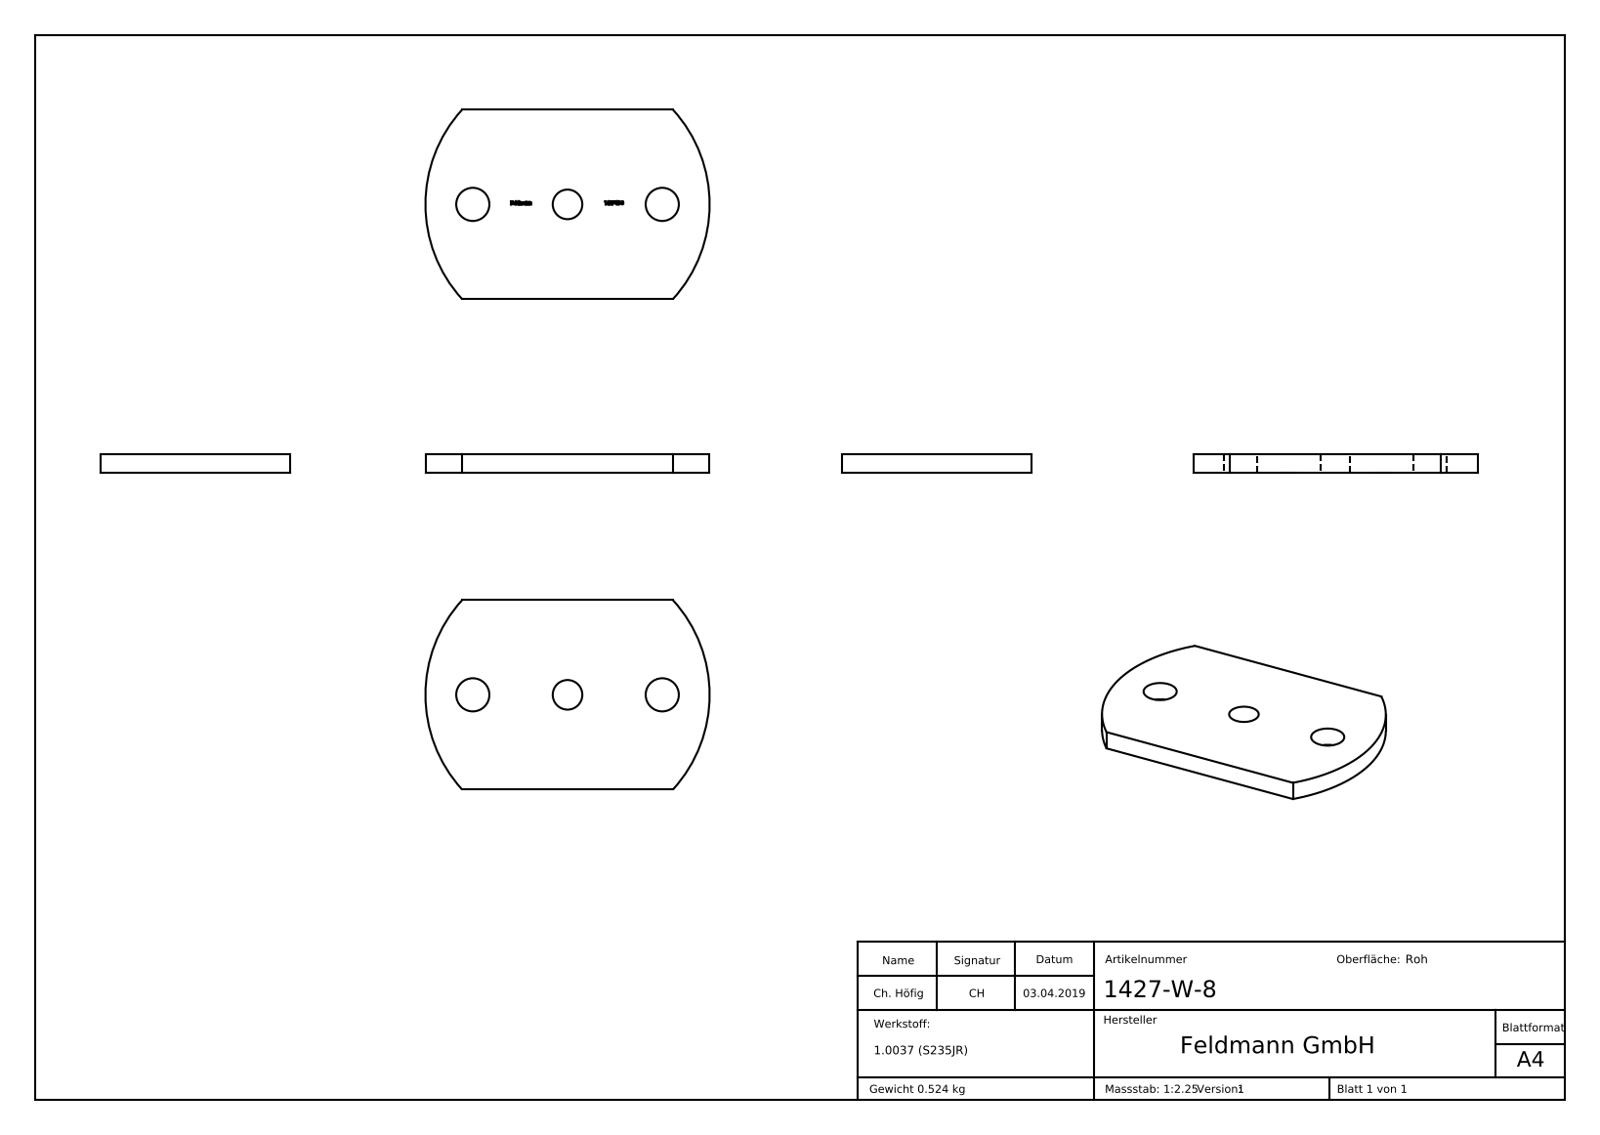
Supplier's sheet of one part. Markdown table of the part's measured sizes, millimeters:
| quantity | value |
| --- | --- |
| part name | 1427-W-8 |
| STEP written by | SolidWorks 2015 (CONFIG_CONTROL_DESIGN) |
| units | millimeters |
| bodies | 1 solid, 211 faces (132 planar, 8 cylindrical, 71 other) |
| overall size | 120 × 80 × 8 |
| volume | 67 130 mm³ |
| surface area | 20 638 mm² |
| round holes (diameter × count) | 14 × 2, 12.5 × 1 |
| partial cylindrical surfaces (radius × count) | 59.36 × 2 |
| main face-to-face distances | 8, 80, 7.9, 1.24, 1.12, 37.98, 2.03, 0.54, 40.01, 36.74 |
| hole center spacings | 40, 80 |
